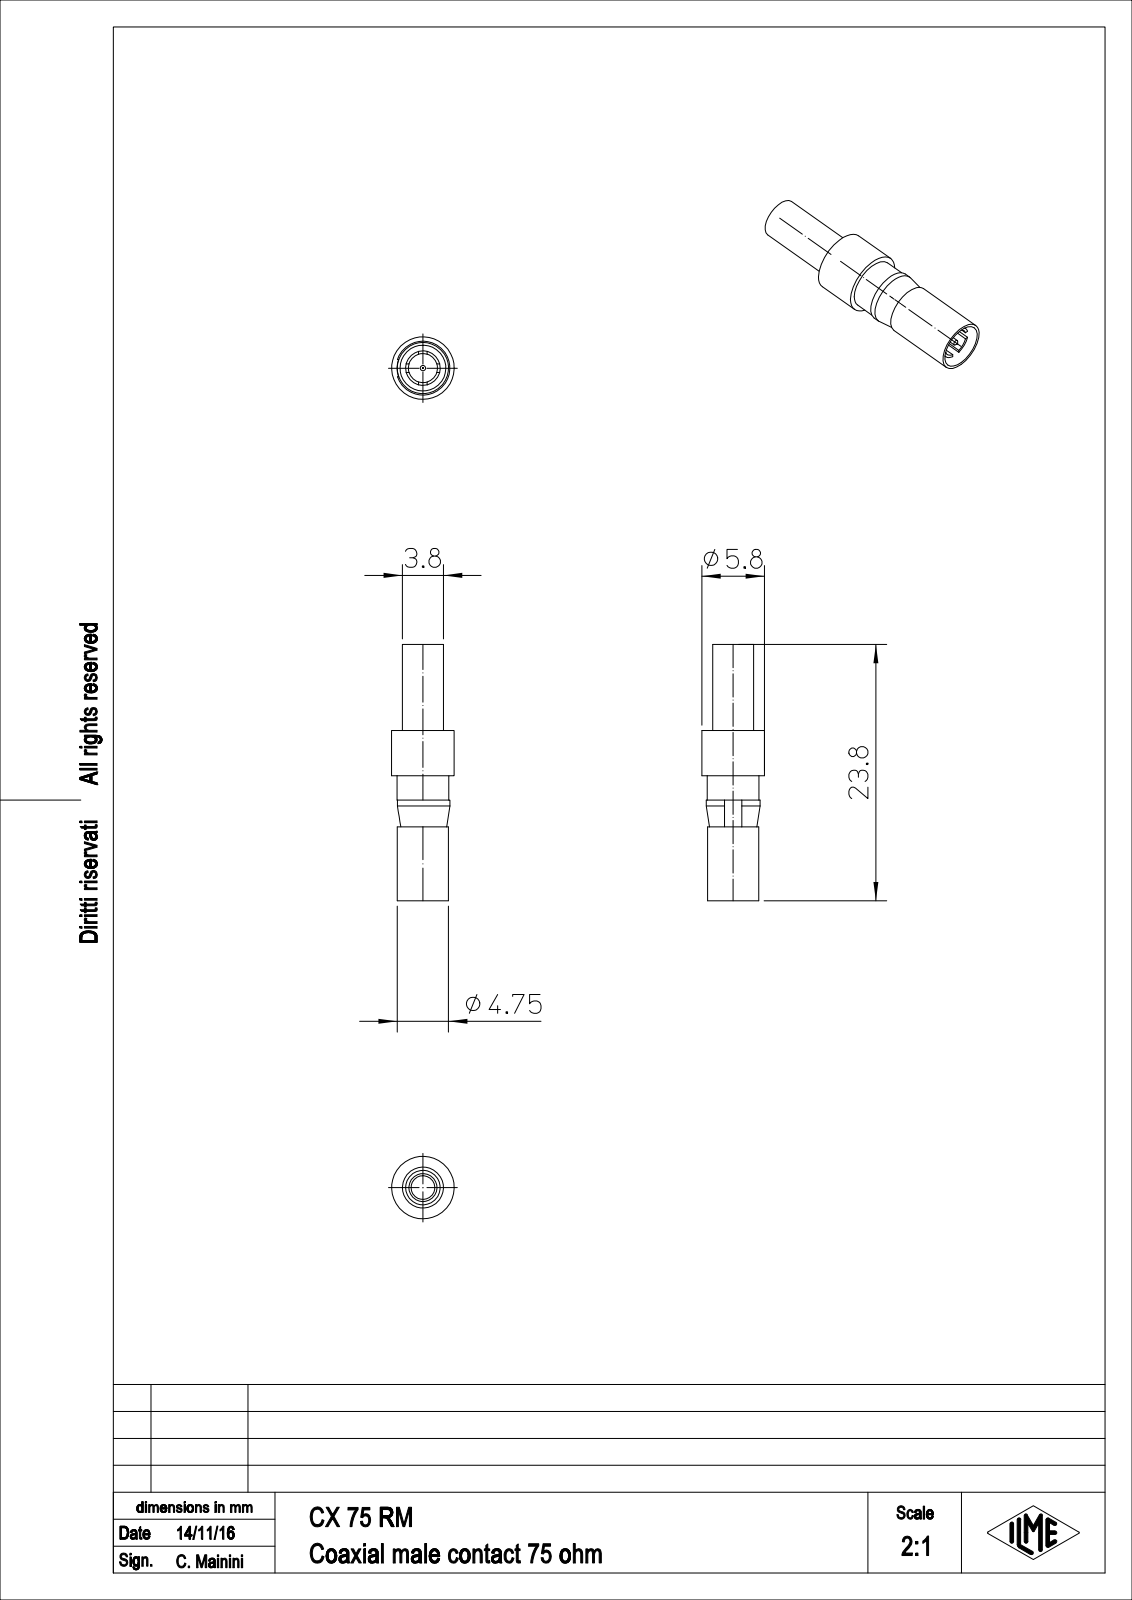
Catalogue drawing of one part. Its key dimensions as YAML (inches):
part_name: "CX_75_RM"
step_written_by: "PTC Creo Elements/Direct Modeling 19.0E 27-Jun-2016 (C) Parametric Technology GmbH (AUTOMOTIVE_DESIGN)"
units: inches
bodies: {solids: 1, faces: 58, planar: 31, cylindrical: 24, other: 3}
overall_size: [0.937, 0.228, 0.228]
volume: 0.015
surface_area: 1.2
round_holes:
  - {diameter: 0.087, count: 1}
  - {diameter: 0.106, count: 1}
  - {diameter: 0.126, count: 1}
  - {diameter: 0.167, count: 1}
round_bosses_or_shafts:
  - {diameter: 0.228, count: 1}
  - {diameter: 0.197, count: 1}
  - {diameter: 0.189, count: 1}
  - {diameter: 0.187, count: 1}
  - {diameter: 0.15, count: 1}
  - {diameter: 0.102, count: 1}
  - {diameter: 0.02, count: 1}
partial_cylinders:
  - {radius: 0.069, count: 1}
face_to_face_distances: [0.197, 0.362, 0.165, 0.031, 0.622, 0.457, 0.26, 0.016, 0.047, 0.315]
